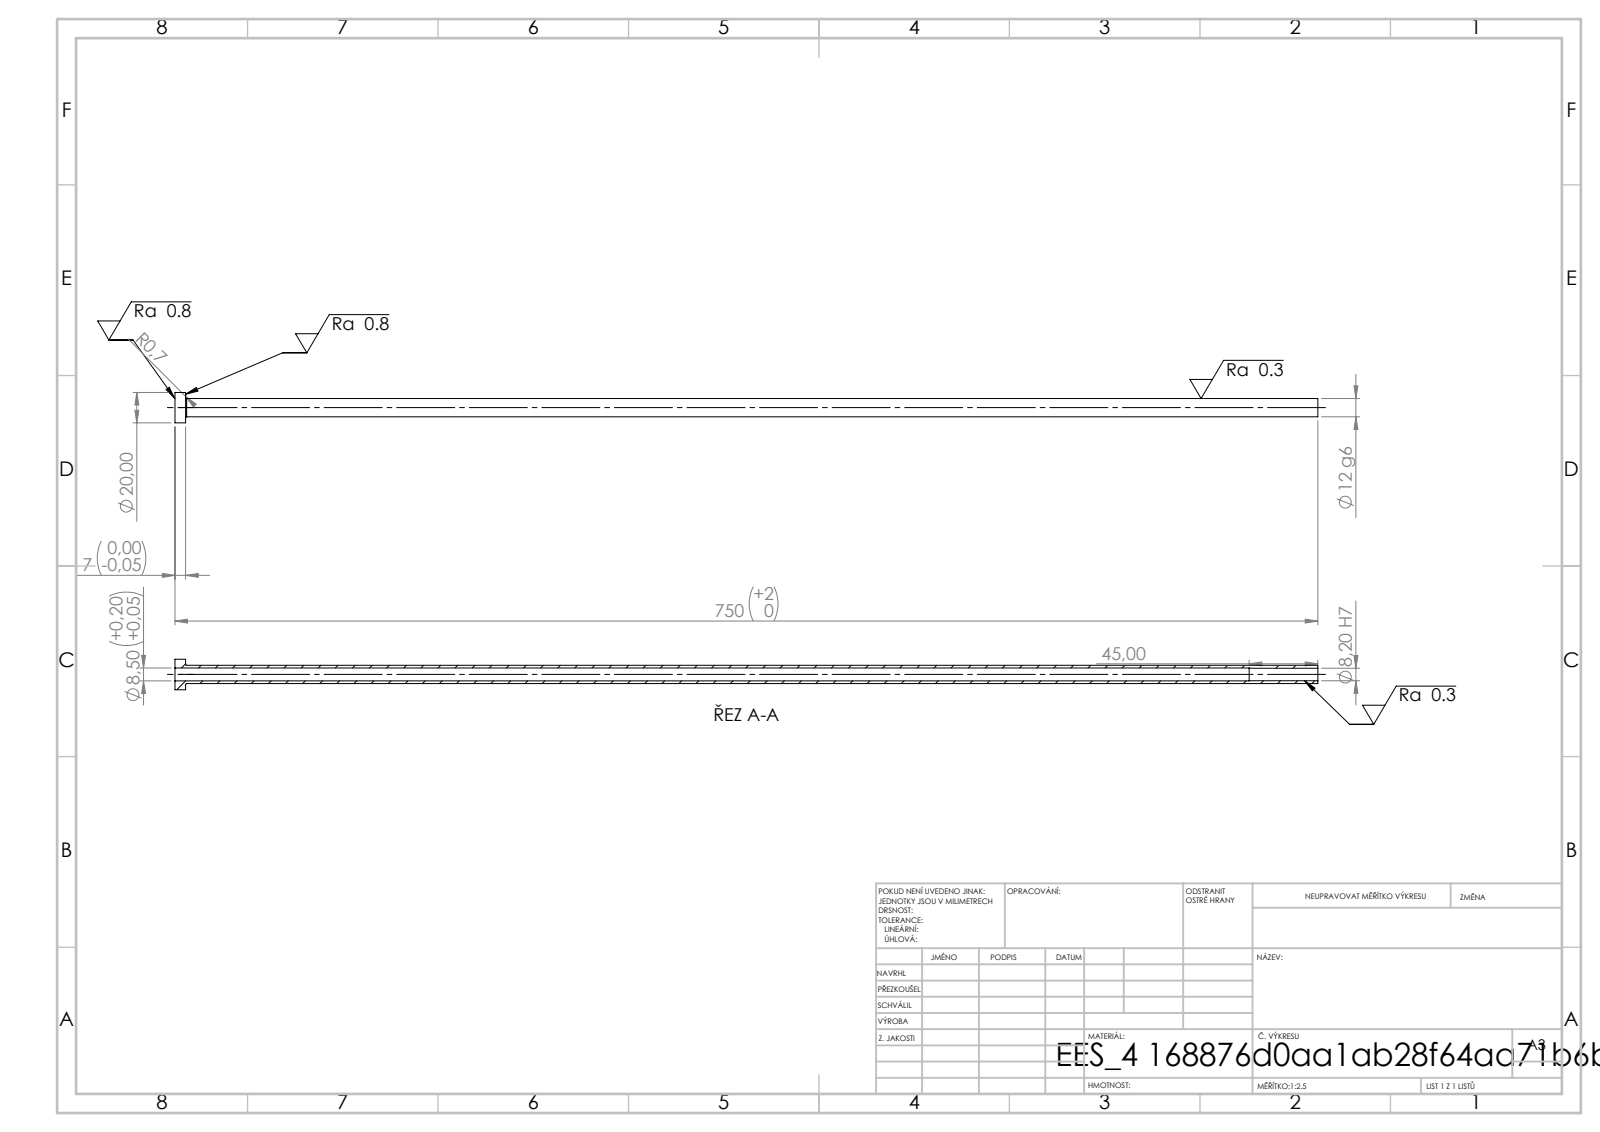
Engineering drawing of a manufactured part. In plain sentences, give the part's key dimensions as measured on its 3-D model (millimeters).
Its 3-D file was written by "SolidWorks 2019 (CONFIG_CONTROL_DESIGN)". It is 1 solid with 14 faces: 4 planar, 8 cylindrical and 2 other. Overall it measures 750 by 20 by 20 millimeters. Its volume is 43 853 cubic millimeters and its surface area 48 947 square millimeters. Round holes: 1 of diameter 8.2, 1 of diameter 8.5. Round bosses or shafts: 1 of diameter 20, 1 of diameter 12. The main face-to-face distances are 7, 750, 743, 705, 698, 45.
